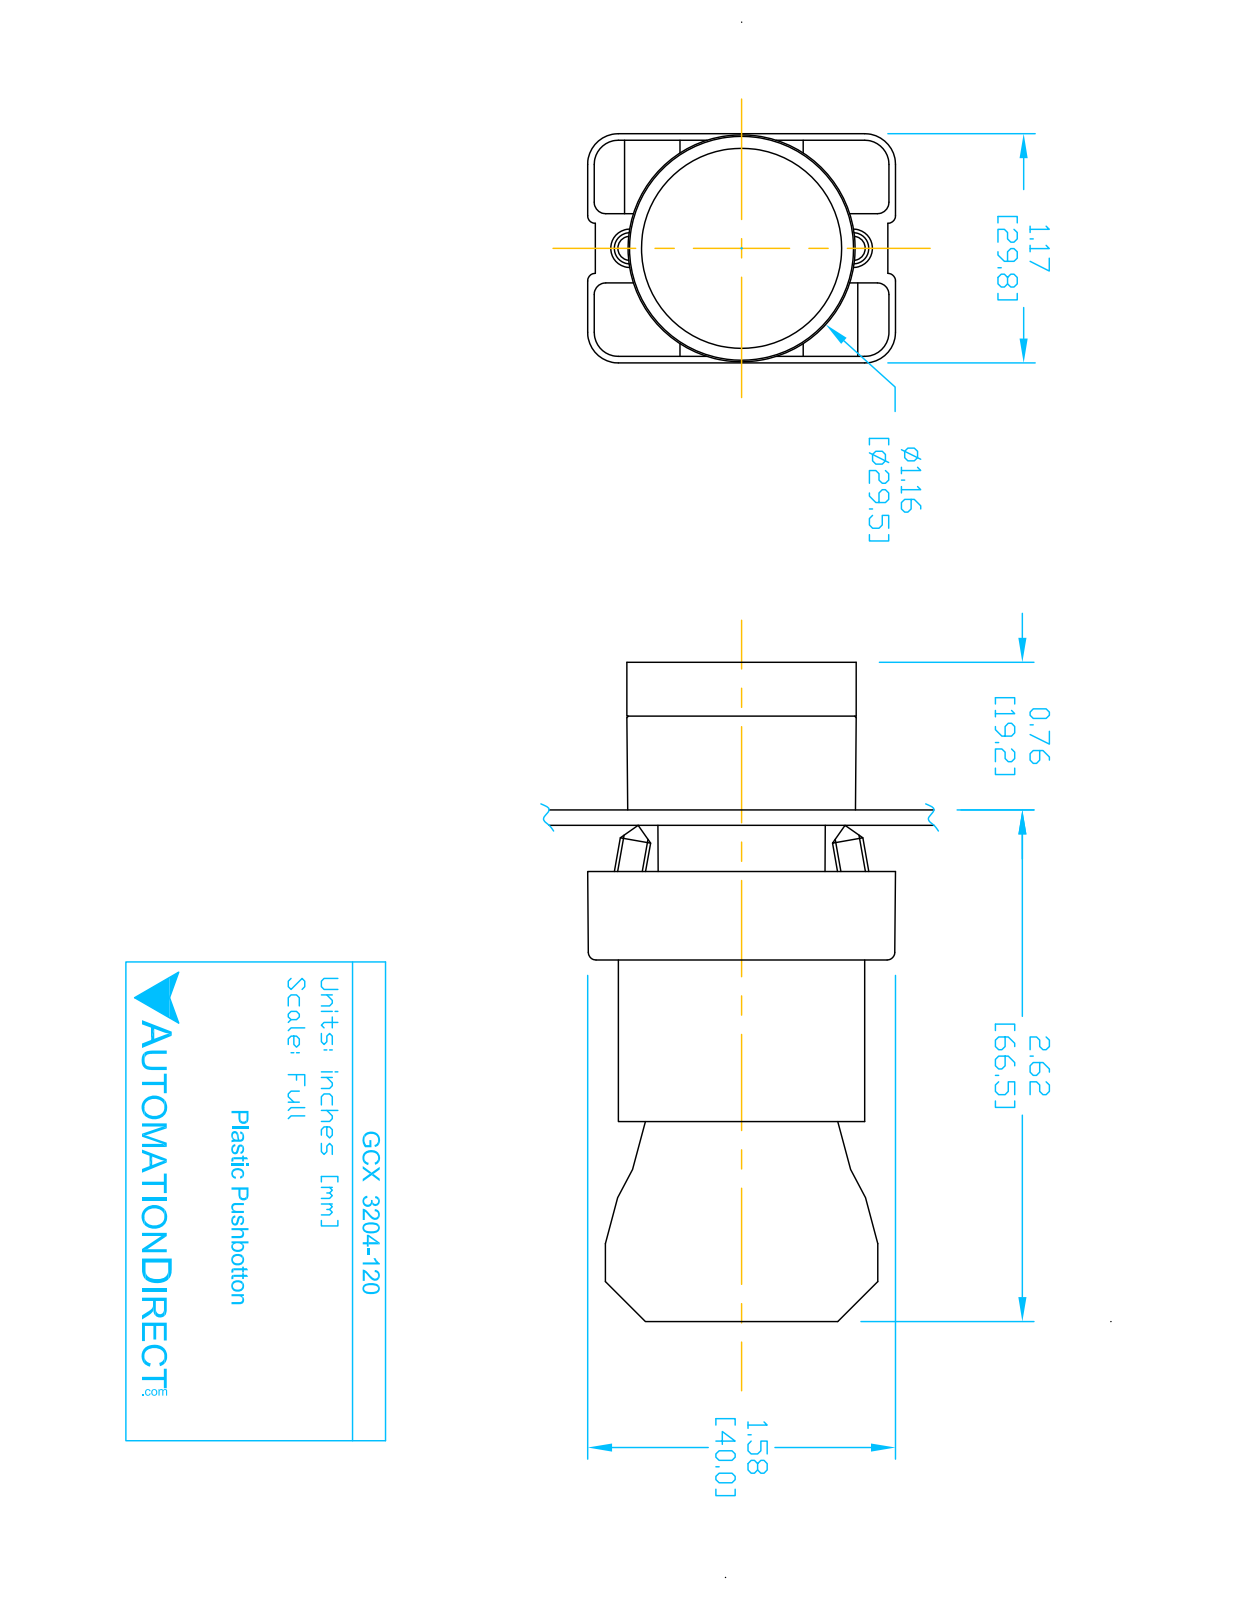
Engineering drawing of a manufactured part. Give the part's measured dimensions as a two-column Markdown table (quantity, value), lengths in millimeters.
| quantity | value |
| --- | --- |
| part name | GCX3204-120; ecx1040; ECX1050; ECX3029-2 (+1 more) |
| STEP written by | SolidWorks 2016 (AUTOMOTIVE_DESIGN) |
| units | millimeters |
| bodies | 8 solids, 431 faces (252 planar, 148 cylindrical, 31 other) |
| overall size | 84.3 × 40.2 × 29.9 |
| volume | 45 790 mm³ |
| surface area | 25 010 mm² |
| round holes (diameter × count) | 2 × 2, 3.1 × 2, 3.3 × 2, 2.2 × 1, 5 × 1, 11.9 × 1, 22.3 × 1, 22.6 × 1, 26 × 1 |
| round bosses / shafts (diameter × count) | 4 × 4, 29.8 × 1, 25.5 × 1, 24 × 1, 21.7 × 1, 19.8 × 1, 12.8 × 1 |
| partial cylindrical surfaces (radius × count) | 1.5 × 24, 1 × 12, 3.1 × 12, 4 × 12, 1 × 8, 3.3 × 2, 0.5 × 1, 1.6 × 1 |
| main face-to-face distances | 21, 14.7, 51.3, 30.3, 29.7, 7, 58.3, 37.3, 0.8, 0.8 |
| hole center spacings | 6, 13.8, 12, 12.4 |
